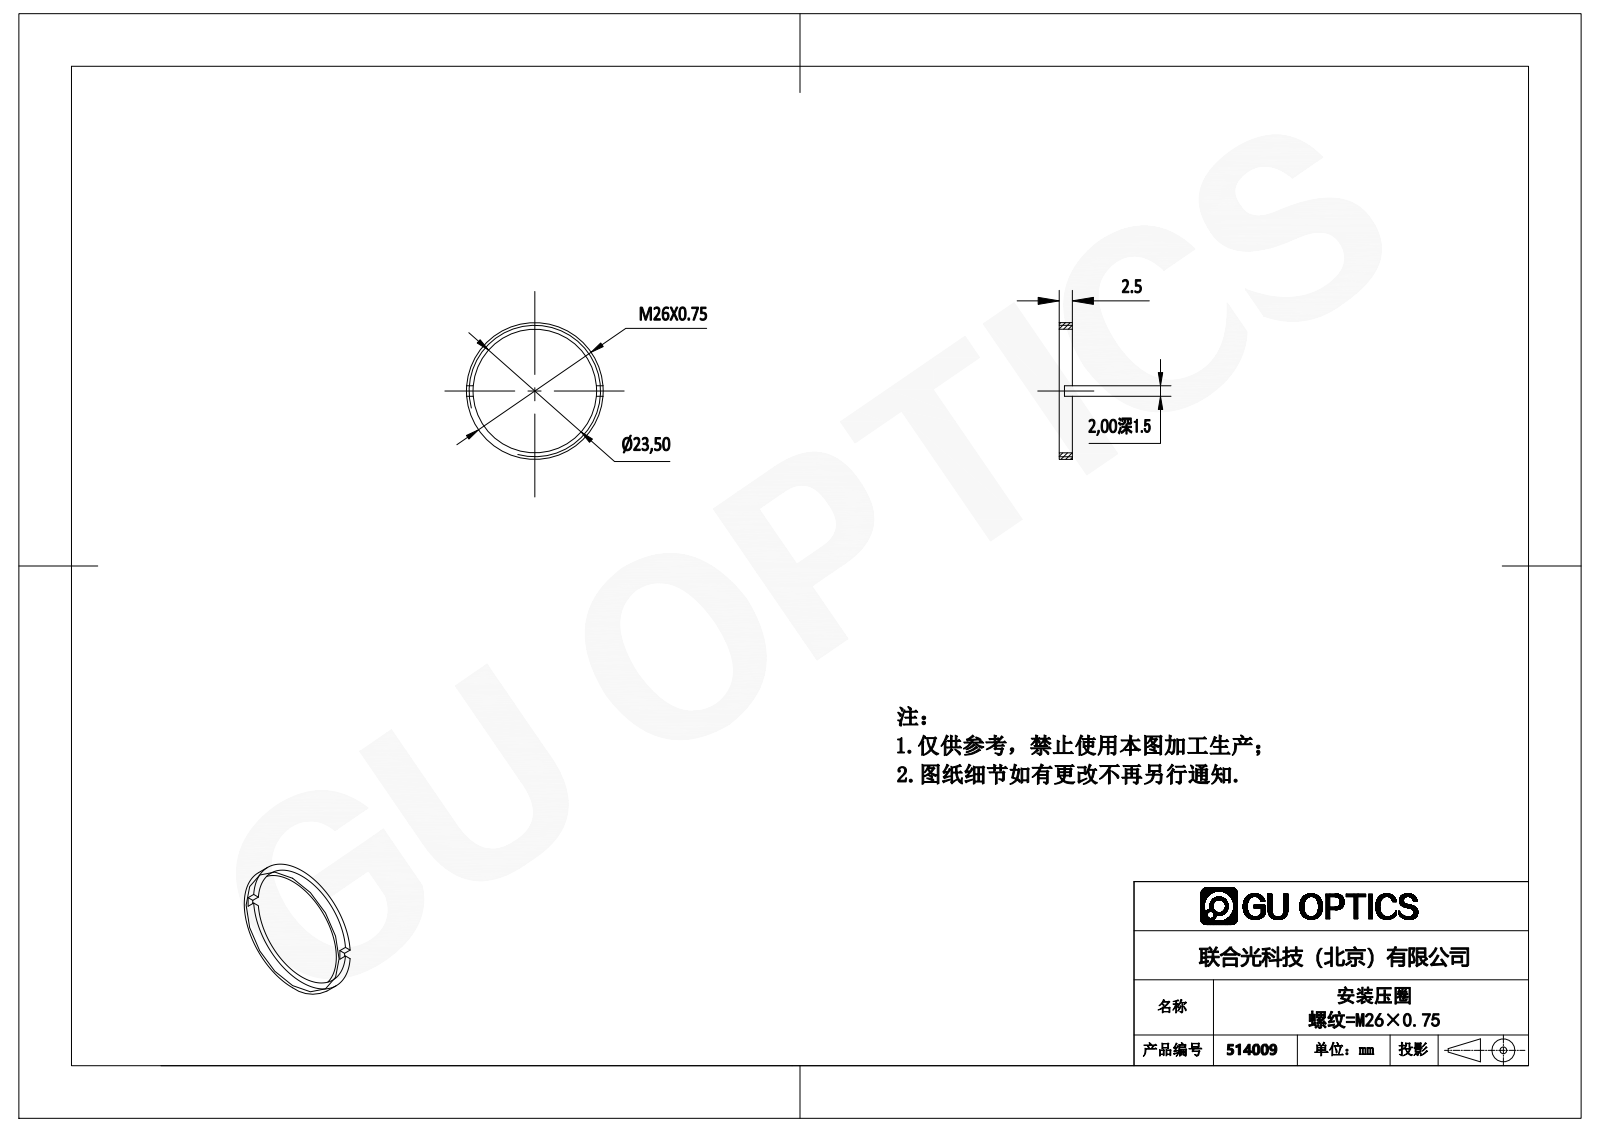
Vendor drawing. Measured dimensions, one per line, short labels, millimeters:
name: 514009
written by: SolidWorks 2016 (AUTOMOTIVE_DESIGN)
unit: mm
bodies: 1 solid, 13 faces (9 planar, 4 cylindrical, 0 other)
size: 25 × 25 × 2.5
volume: 138 mm³; area: 488 mm²
holes: 1× ⌀23.5
bosses: 1× ⌀25
face distances: 2.5, 1, 1.5, 2
